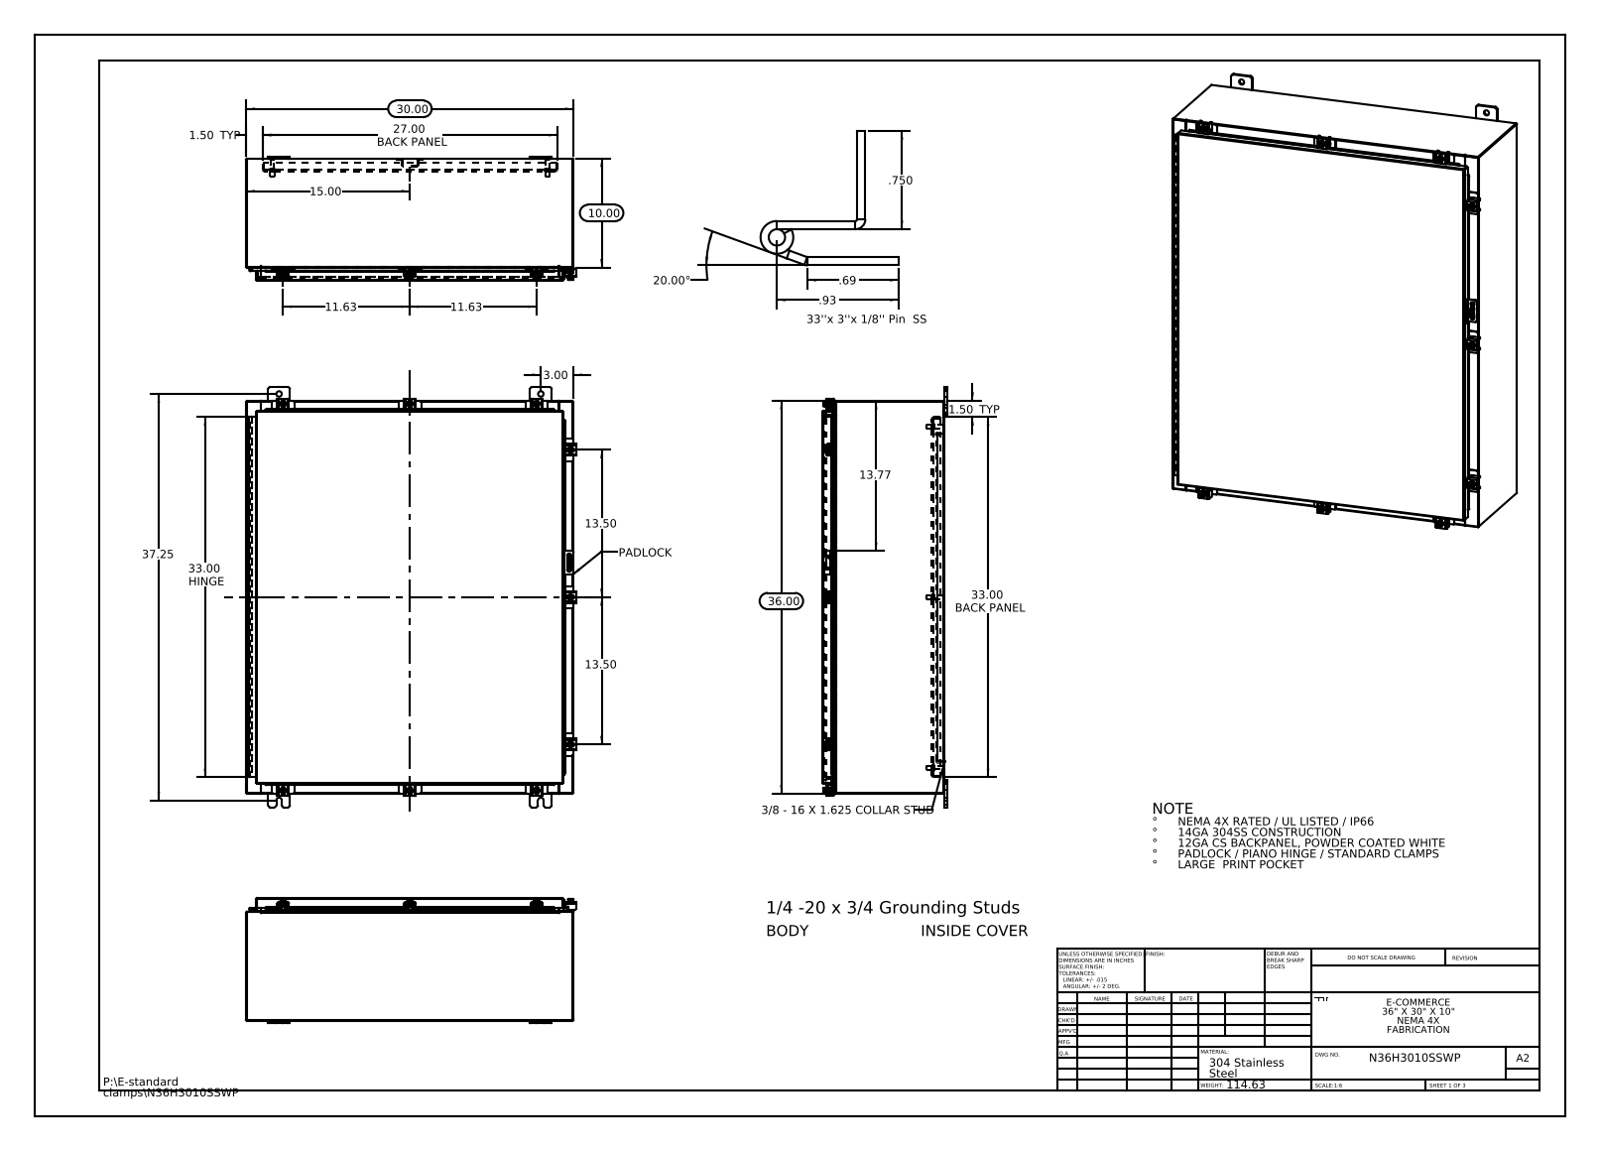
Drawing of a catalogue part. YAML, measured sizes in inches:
part_name: "N36H3010SSWP Mounting Feet; N36H3010SSWP Body; N36H3010SSWP 22101002; N36H3010SSWP Hinge Cover Side (+8 more)"
step_written_by: "SolidWorks 2013 (CONFIG_CONTROL_DESIGN)"
units: inches
bodies: {solids: 65, faces: 2456, planar: 1288, cylindrical: 1028, other: 140}
overall_size: [38.5, 30.211, 11.389]
volume: 402.1
surface_area: 10045
round_holes:
  - {diameter: 0.5, count: 10}
  - {diameter: 0.213, count: 9}
  - {diameter: 0.26, count: 9}
  - {diameter: 0.125, count: 2}
  - {diameter: 0.125, count: 1}
round_bosses_or_shafts:
  - {diameter: 0.25, count: 10}
  - {diameter: 0.5, count: 9}
  - {diameter: 0.399, count: 9}
  - {diameter: 0.625, count: 6}
  - {diameter: 0.375, count: 6}
  - {diameter: 0.33, count: 6}
partial_cylinders:
  - {radius: 0.06, count: 42}
  - {radius: 0.013, count: 31}
  - {radius: 0.088, count: 25}
  - {radius: 0.19, count: 24}
  - {radius: 0.12, count: 18}
  - {radius: 0.141, count: 18}
  - {radius: 0.05, count: 13}
  - {radius: 0.08, count: 12}
face_to_face_distances: [0.075, 11.126, 11.051, 11.201, 0.104, 1, 10.126, 1.075, 10.051, 1.179]
hole_center_spacings: [15.625, 17.754, 29.694, 33.366, 37.309, 25.25, 35.451, 1.858]
